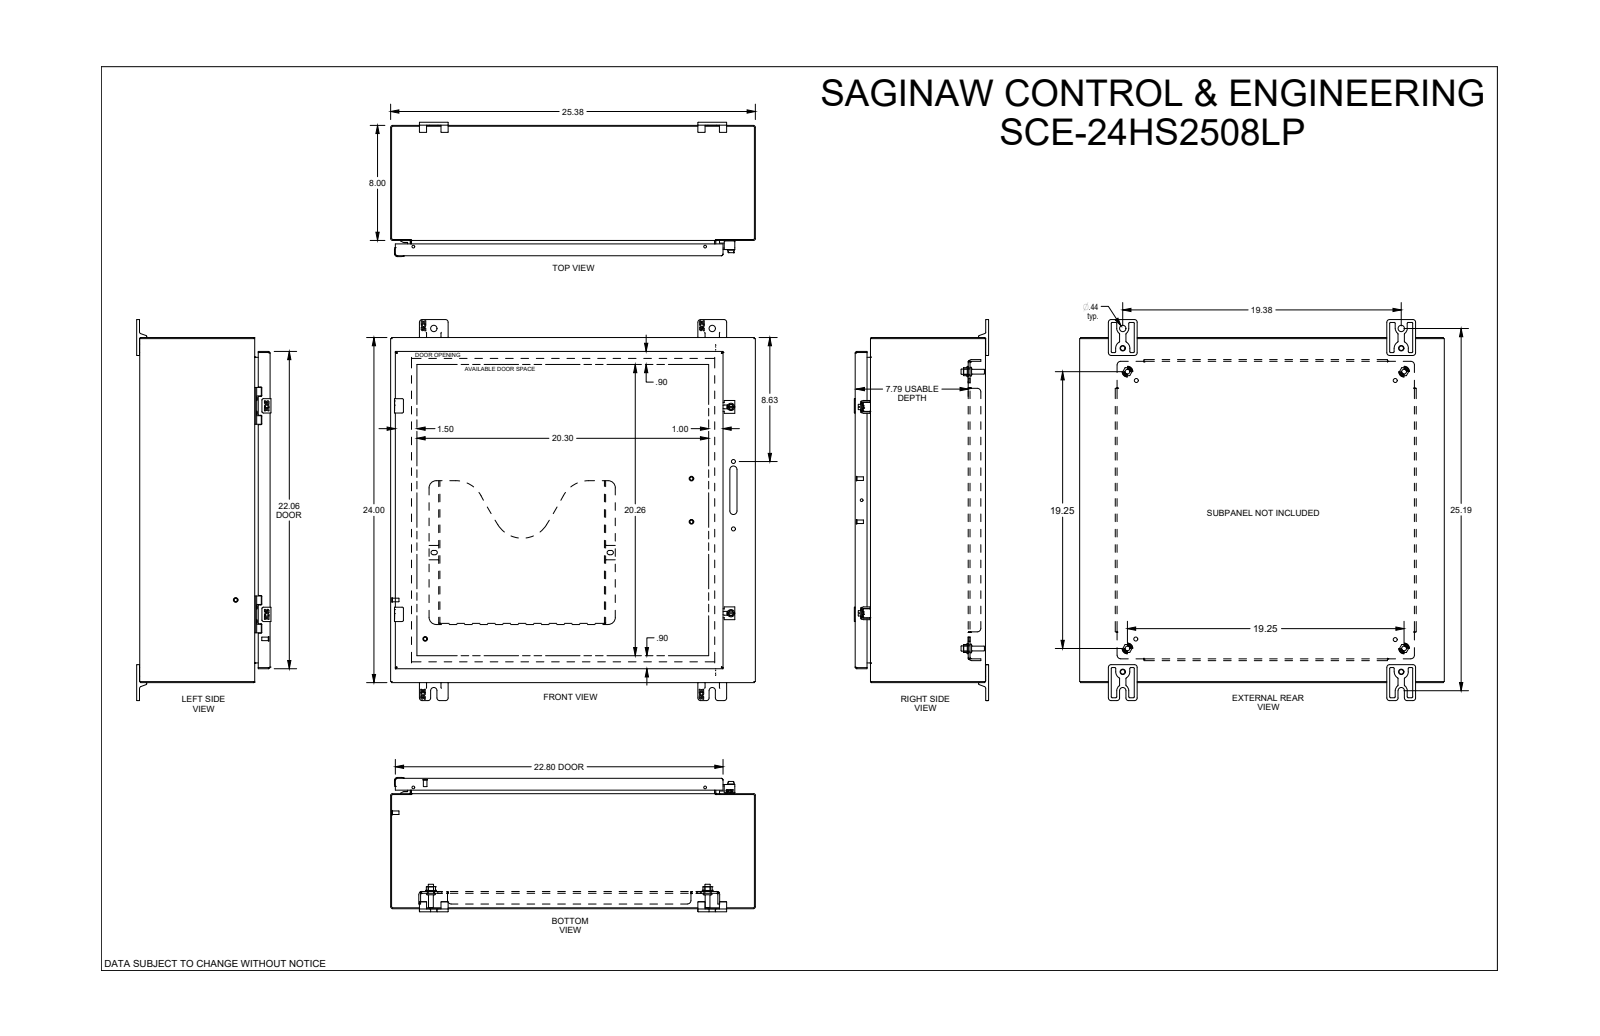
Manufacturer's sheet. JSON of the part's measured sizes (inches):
{"part_name": "SCE-24HS2508LP", "step_written_by": "SolidWorks 2021 (AUTOMOTIVE_DESIGN)", "units": "inches", "bodies": {"solids": 58, "faces": 3386, "planar": 1201, "cylindrical": 863, "other": 1322}, "overall_size": [26.5, 25.375, 9.343], "volume_in3": 257.7, "surface_area_in2": 5922, "round_holes": [[0.281, 6], [0.172, 4], [0.205, 4], [0.244, 4], [0.25, 4], [0.31, 4], [0.312, 4], [0.367, 4], [0.375, 4], [0.5, 4], [0.04, 2], [0.156, 2]], "round_bosses_or_shafts": [[0.248, 8], [0.25, 6], [0.17, 6], [0.59, 4], [0.563, 4], [0.376, 4], [0.366, 4], [0.332, 4]], "partial_cylinders_radius": [[0.01, 107], [0.025, 72], [0.015, 24], [0.029, 24], [0.185, 21], [0.04, 18], [0.043, 12], [0.118, 12]], "face_to_face_distances": [0.075, 8.993, 8.918, 1.125, 1.2, 7.868, 7.793, 9.068, 0.125, 1.075], "hole_center_spacings": [14.5, 0.875, 18.641, 19.375, 0.493, 0.494, 0.516, 0.984]}
